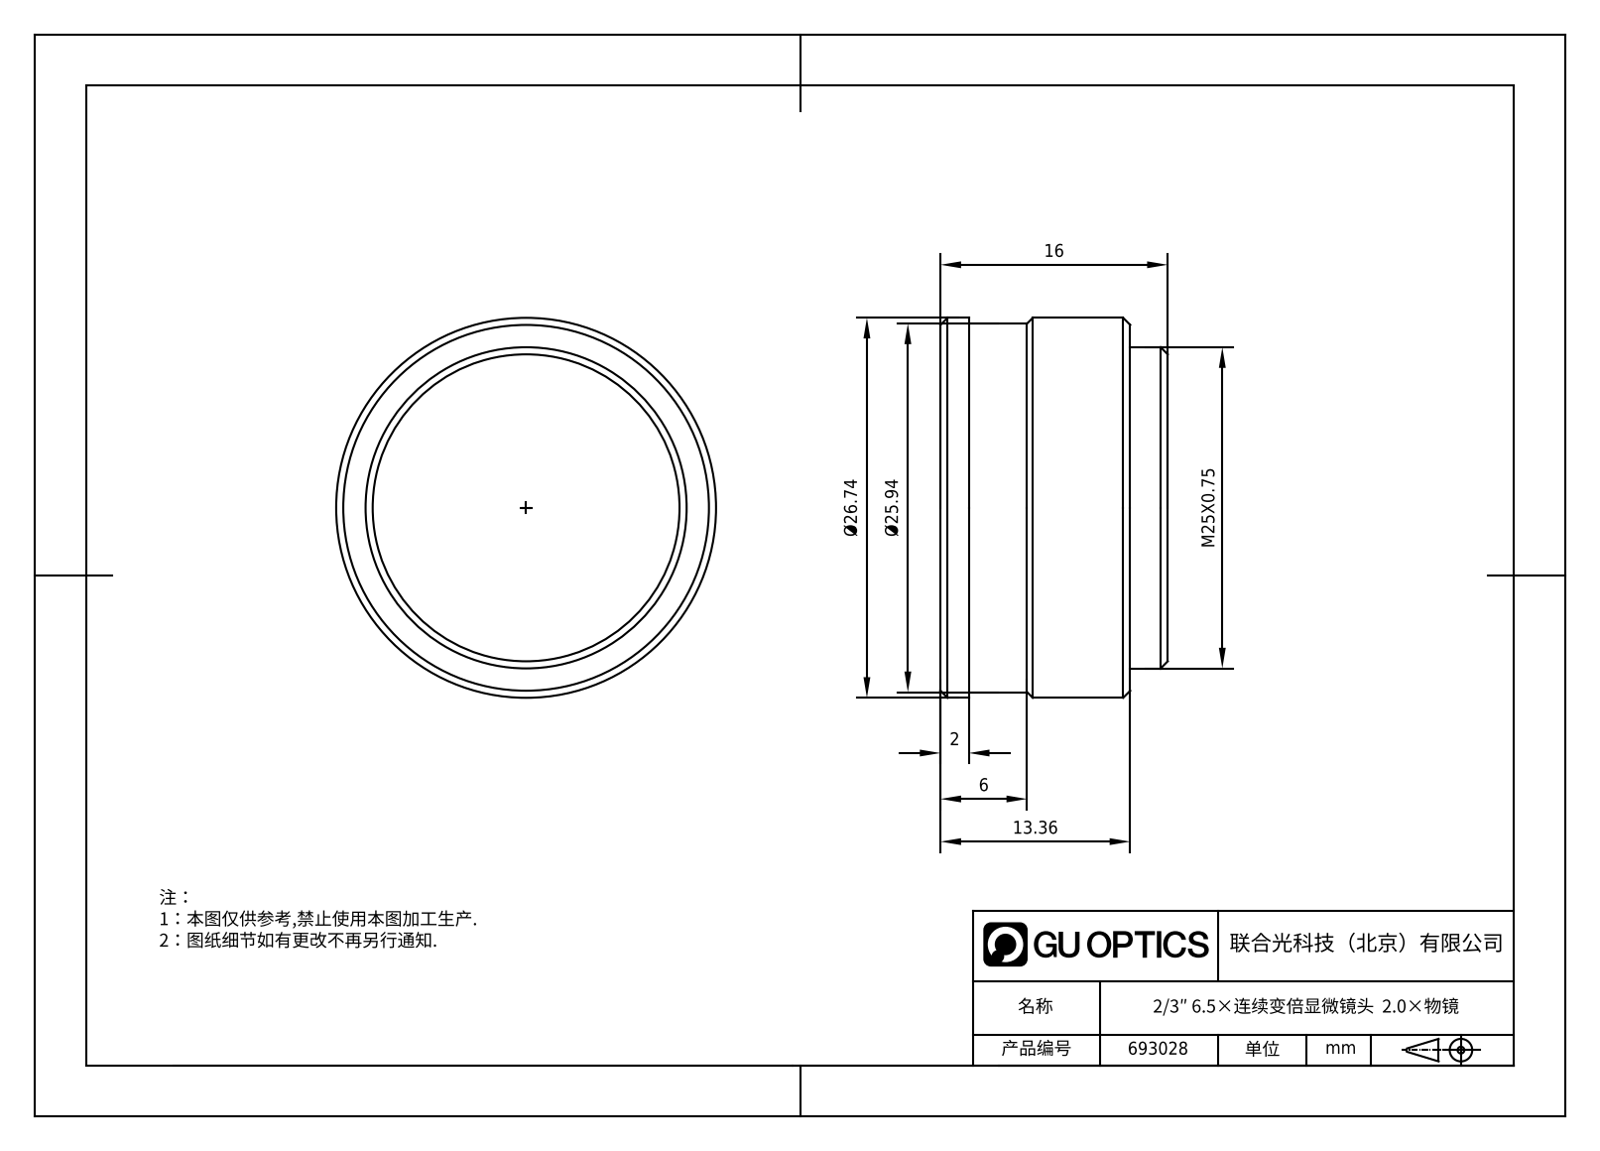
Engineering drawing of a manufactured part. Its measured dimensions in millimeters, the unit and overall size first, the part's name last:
Units: millimetres
Overall size (bounding box): 26.74 × 26.74 × 14.95
Round holes (diameter × count): ⌀12.8 ×1, ⌀17.6 ×1, ⌀20 ×1, ⌀21 ×1, ⌀24.19 ×1
Round bosses / shafts (diameter × count): ⌀26.74 ×1, ⌀25.94 ×1, ⌀22.6 ×1, ⌀19 ×1, ⌀14.2 ×1
Main face-to-face distances: 1, 5.1, 1.2, 0.5, 6.3, 1.5, 13.95, 2, 5.3, 4.1
Volume: 6 191 mm³ · Surface area: 5 757 mm²
Bodies: 3 solids, 79 faces (29 planar, 12 cylindrical, 38 other)
Part name (STEP PRODUCT): 693028
STEP written by: SolidWorks 2020 (CONFIG_CONTROL_DESIGN)
